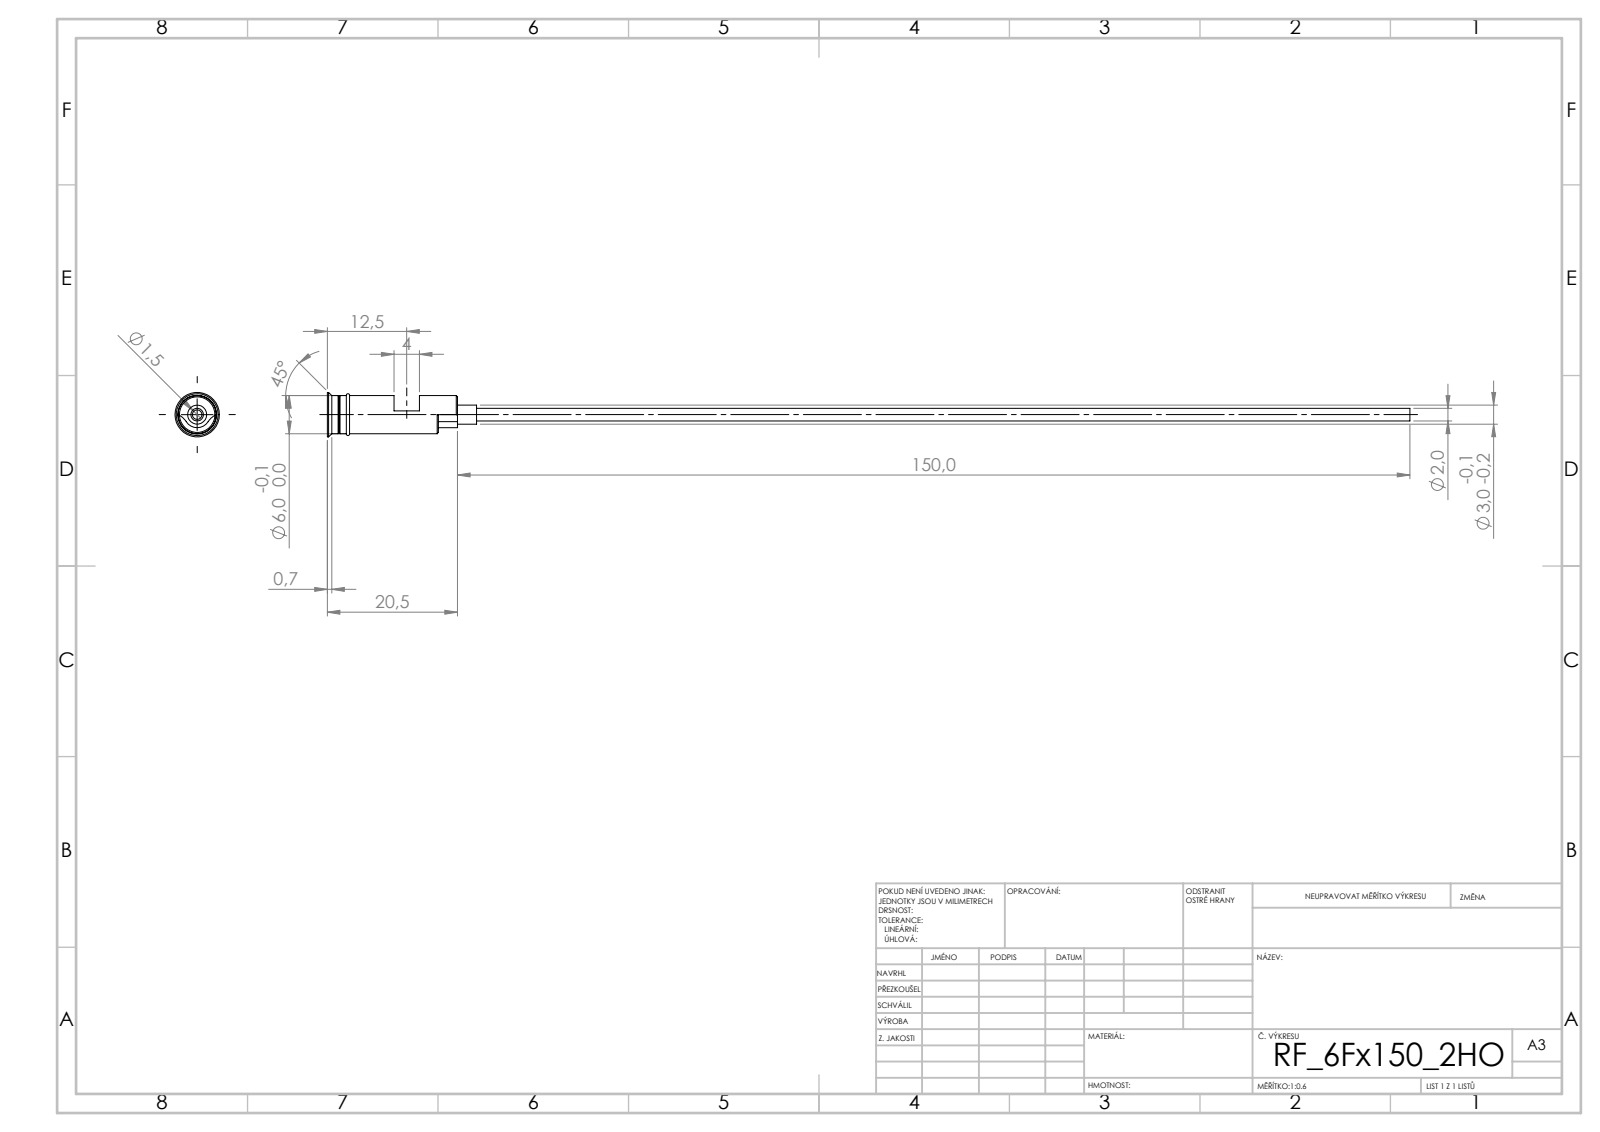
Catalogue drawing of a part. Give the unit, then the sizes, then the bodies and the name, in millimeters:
Units: millimetres
Overall size (bounding box): 170.5 × 7 × 7
Round holes (diameter × count): ⌀1.5 ×1
Round bosses / shafts (diameter × count): ⌀7 ×1, ⌀6 ×1, ⌀5.8 ×1, ⌀3 ×1, ⌀2 ×1
Partial cylindrical surfaces — rounded edges, fillets, slot ends (radius × count): R3 ×2, R2.05 ×1
Main face-to-face distances: 3, 6, 20.5, 10, 10.5, 14.5, 4, 2, 7, 17.5
Volume: 717 mm³ · Surface area: 2 185 mm²
Bodies: 1 solid, 55 faces (24 planar, 19 cylindrical, 12 other)
STEP written by: SolidWorks 2019 (CONFIG_CONTROL_DESIGN)
